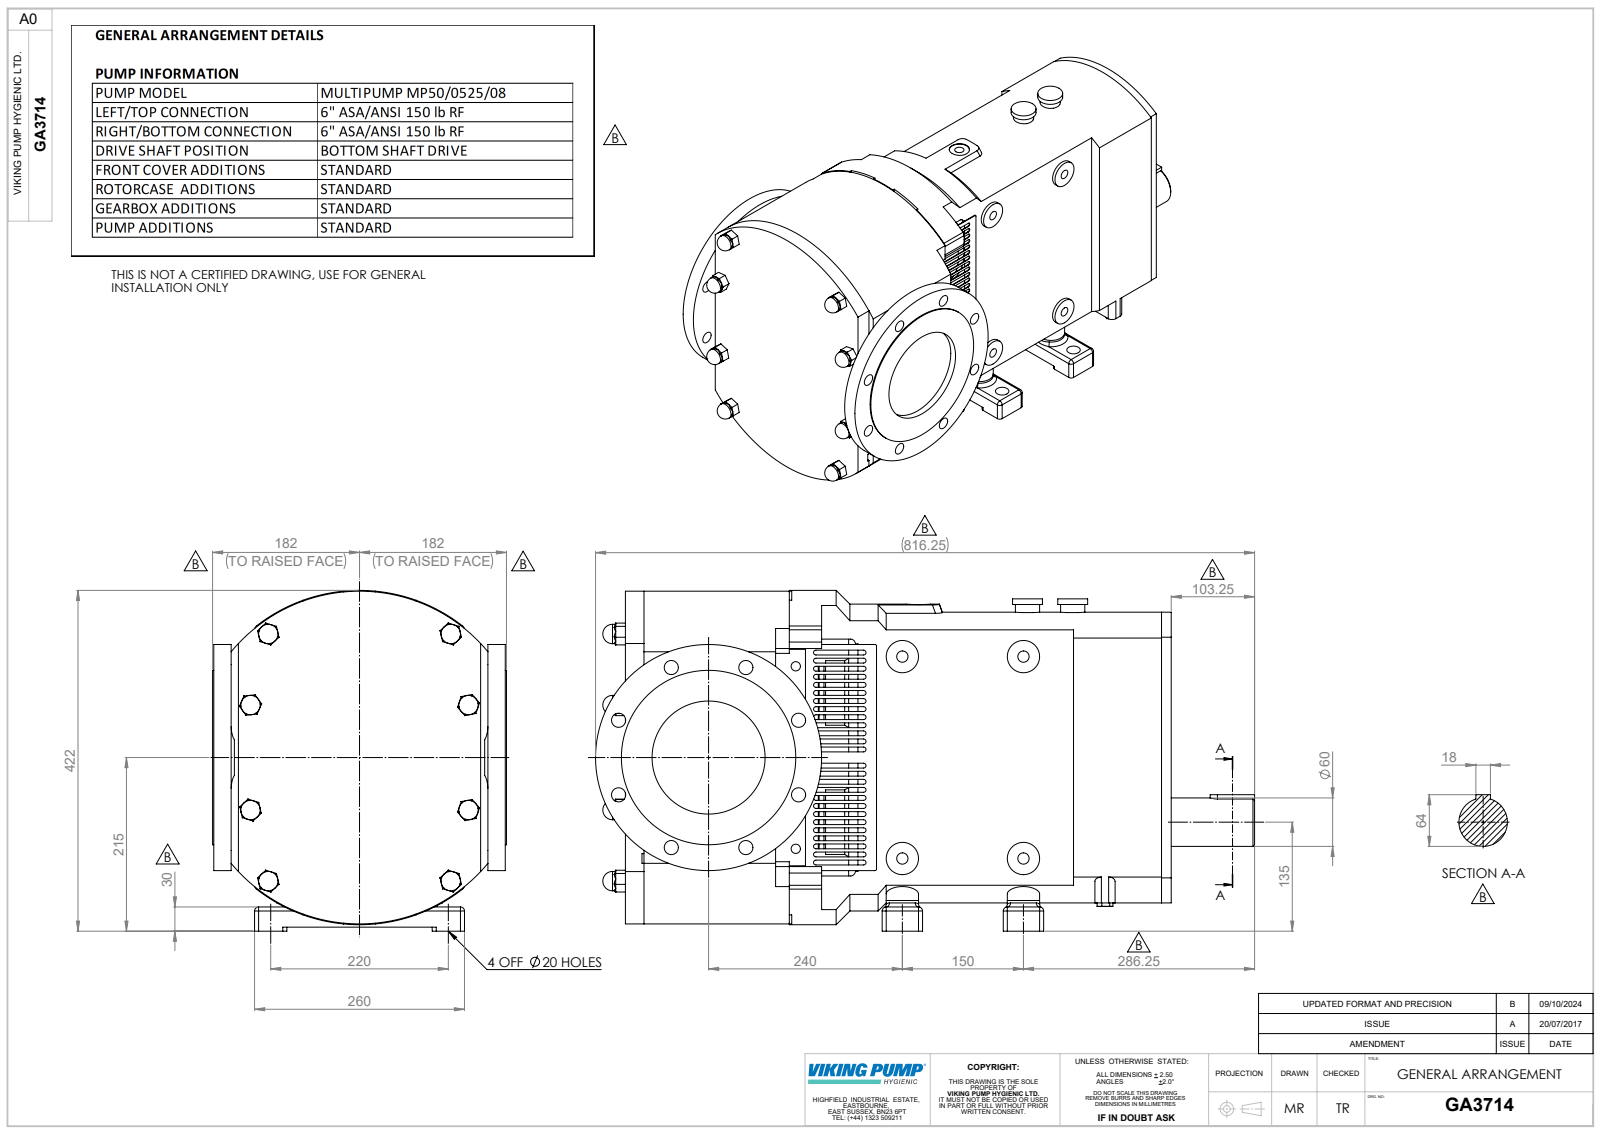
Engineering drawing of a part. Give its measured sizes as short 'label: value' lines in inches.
name: Copy of CP50L-0525 ASA150 H BSD^GA3714; GA3714
written by: SolidWorks 2023 (AUTOMOTIVE_DESIGN)
unit: in
bodies: 1 solid, 1179 faces (517 planar, 407 cylindrical, 255 other)
size: 32.136 × 16.614 × 14.331
volume: 3 295 in³; area: 2 337 in²
holes: 8× ⌀0.689, 4× ⌀0.551, 4× ⌀0.787, 2× ⌀0.453, 2× ⌀1.378, 1× ⌀0.545, 1× ⌀1.181, 1× ⌀5.512
bosses: 8× ⌀1.575, 8× ⌀0.945, 2× ⌀6.654, 2× ⌀3.15, 2× ⌀2.756, 2× ⌀2.677, 2× ⌀1.457, 2× ⌀1.25
rounds: 52× R0.118, 36× R0.197, 22× R0.236, 12× R0.315, 4× R0.079, 1× R0.354, 1× R6.083, 1× R6.496
face distances: 6.772, 26.614, 7.421, 0.65, 7.323, 19.291, 3.071, 3.72, 10.492, 11.142
hole spacings: 4.75, 6.718, 8.777, 3.635, 3.636, 5.906, 9.5, 2.435
